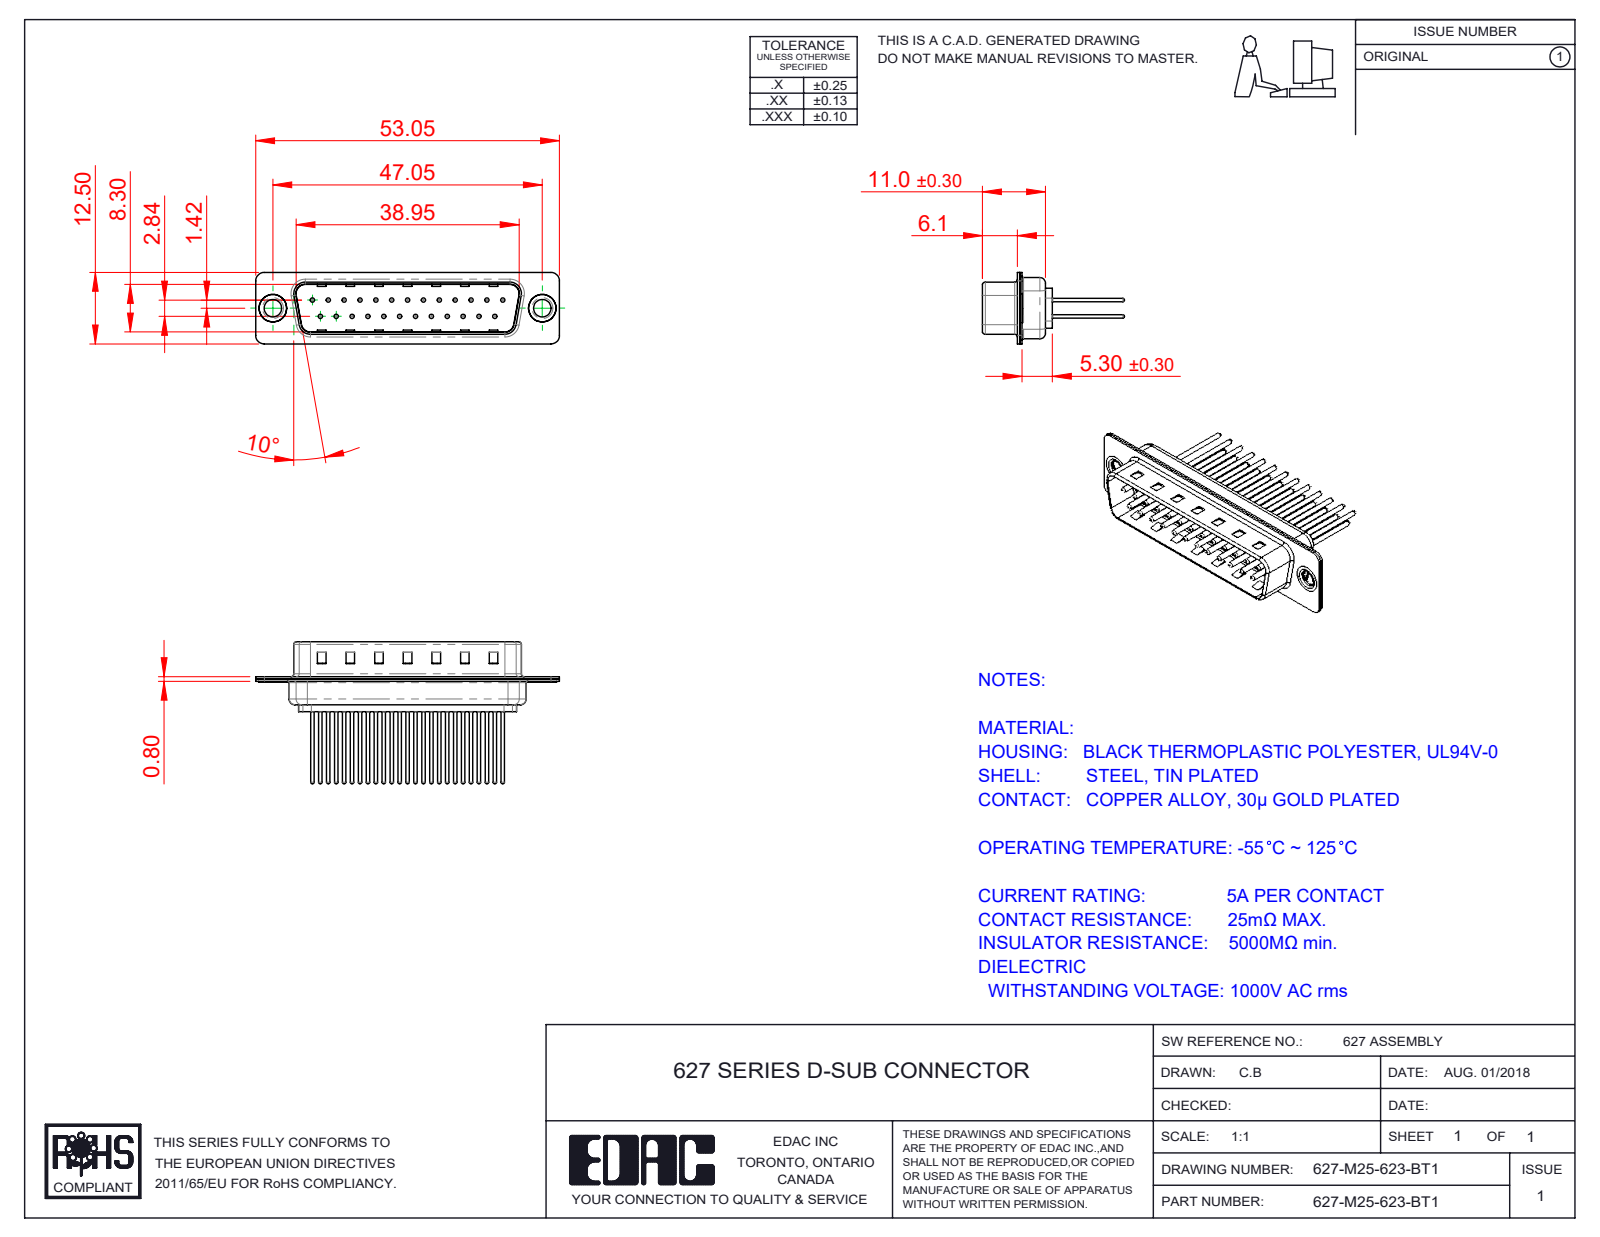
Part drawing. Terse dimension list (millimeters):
name: 627-M25-623-BT1; 627M Thru Hole Rivet; 627M Shell Rear_25 Contacts; 627M Contact Row 2_23 (+3 more)
written by: SolidWorks 2020 (CONFIG_CONTROL_DESIGN)
unit: mm
bodies: 30 solids, 1275 faces (346 planar, 471 cylindrical, 458 other)
size: 53.05 × 24.77 × 12.5
volume: 2 690 mm³; area: 7 022 mm²
holes: 25× ⌀0.75, 25× ⌀1.6, 25× ⌀2, 2× ⌀3.05, 2× ⌀4, 2× ⌀4.8
bosses: 25× ⌀1.5, 25× ⌀0.6, 2× ⌀5, 2× ⌀4.9, 2× ⌀3.55
rounds: 16× R1.5, 12× R2, 8× R0.5, 8× R1.6, 4× R0.25, 4× R0.6, 4× R0.65, 4× R0.9
face distances: 0.4, 0.8, 9.5, 9.1, 8.7, 9.9, 1.2, 6.1, 5.7, 0.75
hole spacings: 3.16, 2.77, 5.54, 8.31, 11.08, 13.85, 16.62, 5.03
